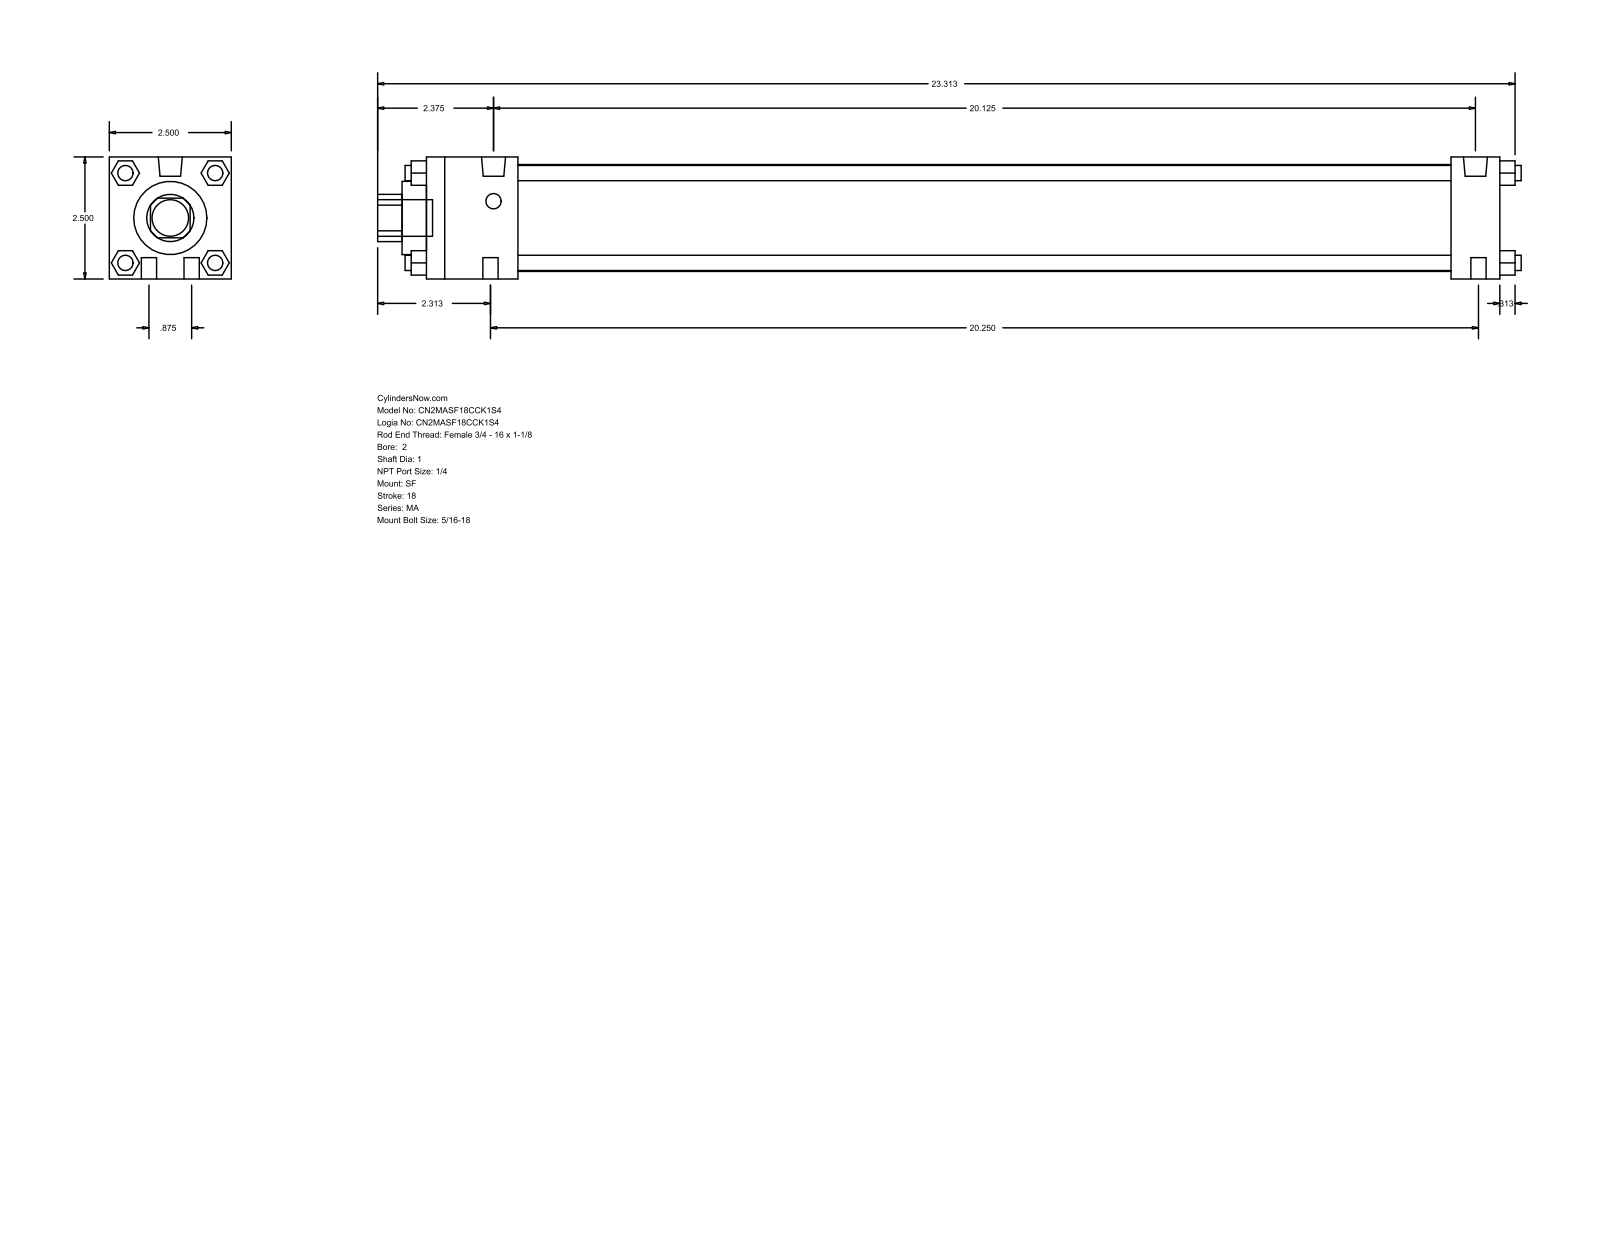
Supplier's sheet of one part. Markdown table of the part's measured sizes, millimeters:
| quantity | value |
| --- | --- |
| part name | MA_SF__0200_1 |
| STEP written by | GSSL Pune (CONFIG_CONTROL_DESIGN) |
| units | millimeters |
| bodies | 0 solids, 124 faces (94 planar, 30 cylindrical, 0 other) |
| overall size | 595.31 × 63.5 × 63.5 |
| round holes (diameter × count) | 25.4 × 1, 38.1 × 1, 55.63 × 1 |
| round bosses / shafts (diameter × count) | 7.94 × 10, 12.49 × 2, 19.05 × 1 |
| partial cylindrical surfaces (radius × count) | 12.29 × 1 |
| main face-to-face distances | 63.5, 558.8, 12.7, 25.4, 533.4, 47.63, 485.77, 511.17, 40.47, 23.37 |
